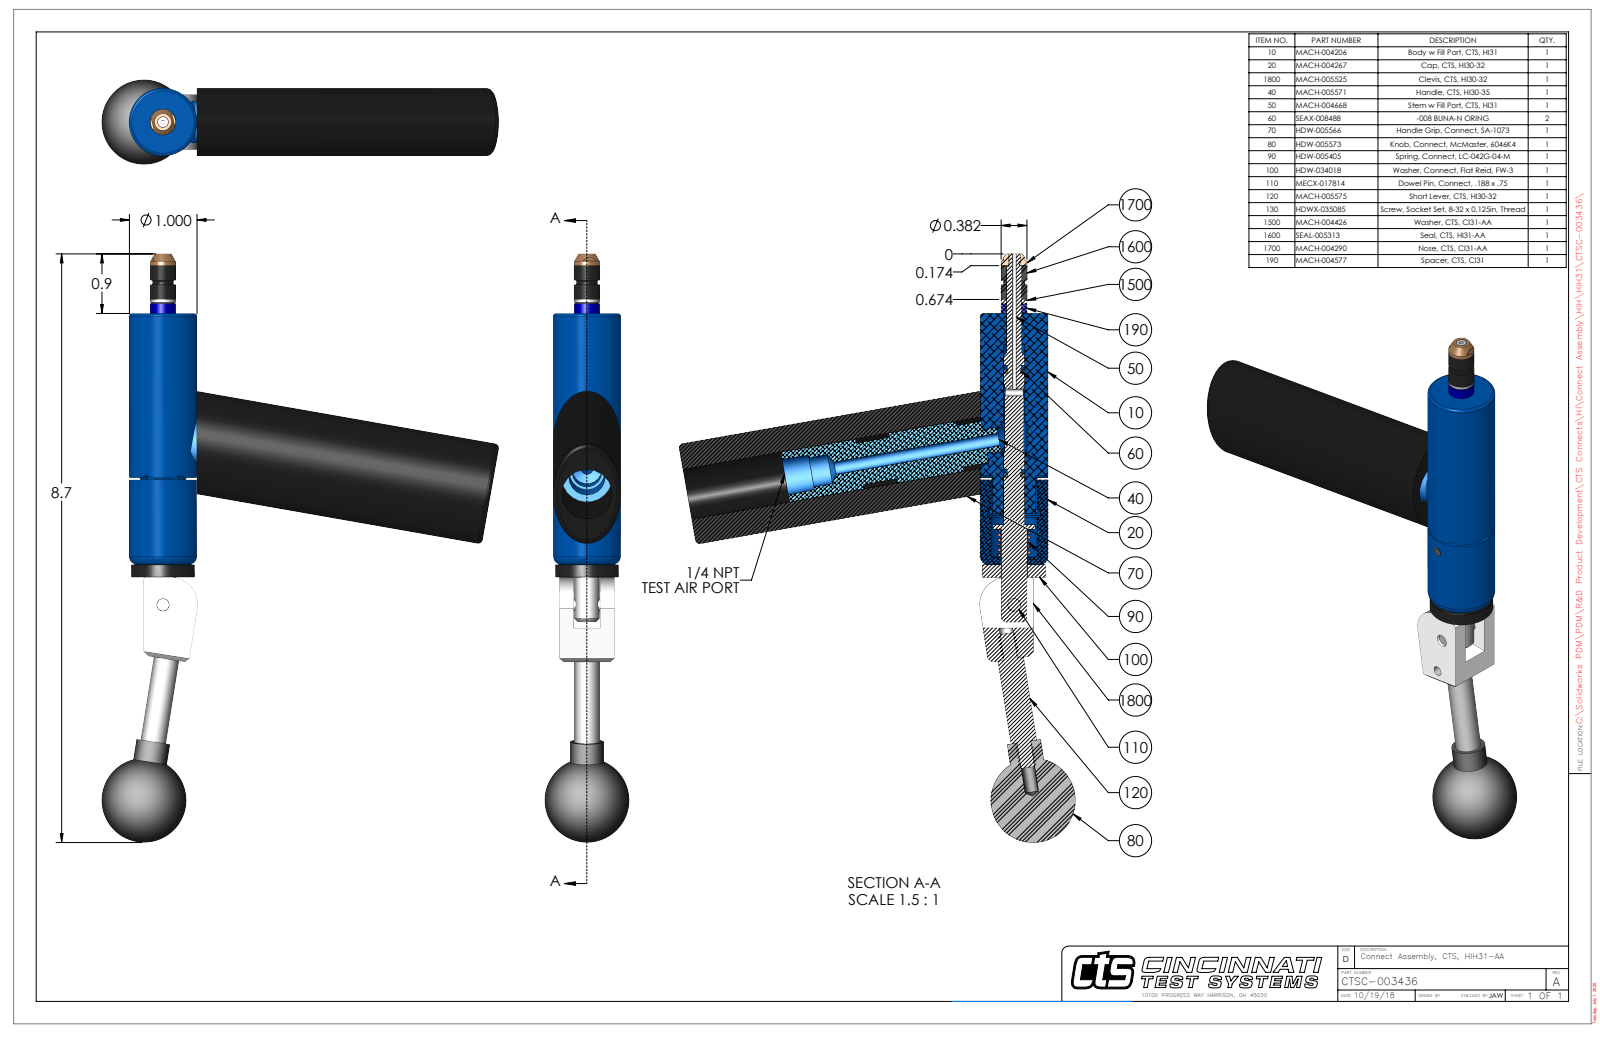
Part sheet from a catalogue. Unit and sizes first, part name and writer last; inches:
Units: inches
Overall size (bounding box): 8.704 × 5.856 × 1.25
Round holes (diameter × count): ⌀0.201 ×2, ⌀0.063 ×1, ⌀0.109 ×1, ⌀0.113 ×1, ⌀0.136 ×1, ⌀0.15 ×1, ⌀0.159 ×1, ⌀0.187 ×1, ⌀0.189 ×1, ⌀0.218 ×1, ⌀0.228 ×1, ⌀0.229 ×1
Round bosses / shafts (diameter × count): ⌀1 ×1, ⌀0.936 ×1, ⌀0.75 ×1, ⌀0.62 ×1, ⌀0.5 ×1, ⌀0.384 ×1, ⌀0.381 ×1, ⌀0.38 ×1
Partial cylindrical surfaces — rounded edges, fillets, slot ends (radius × count): R0.093 ×6, R0.029 ×2, R0.325 ×1, R0.4 ×1, R0.465 ×1, R0.483 ×1
Main face-to-face distances: 0.21, 0.602, 0.812, 0.187, 3.713, 3.901, 0.785, 0.391, 2.46, 1.253
Hole centre spacings: 0.599, 1.658, 2.252
Volume: 9.151 in³ · Surface area: 73.79 in²
Bodies: 11 solids, 294 faces (102 planar, 124 cylindrical, 68 other)
Part name (STEP PRODUCT): CTSC-003436
STEP written by: SolidWorks 2023 (AUTOMOTIVE_DESIGN)
